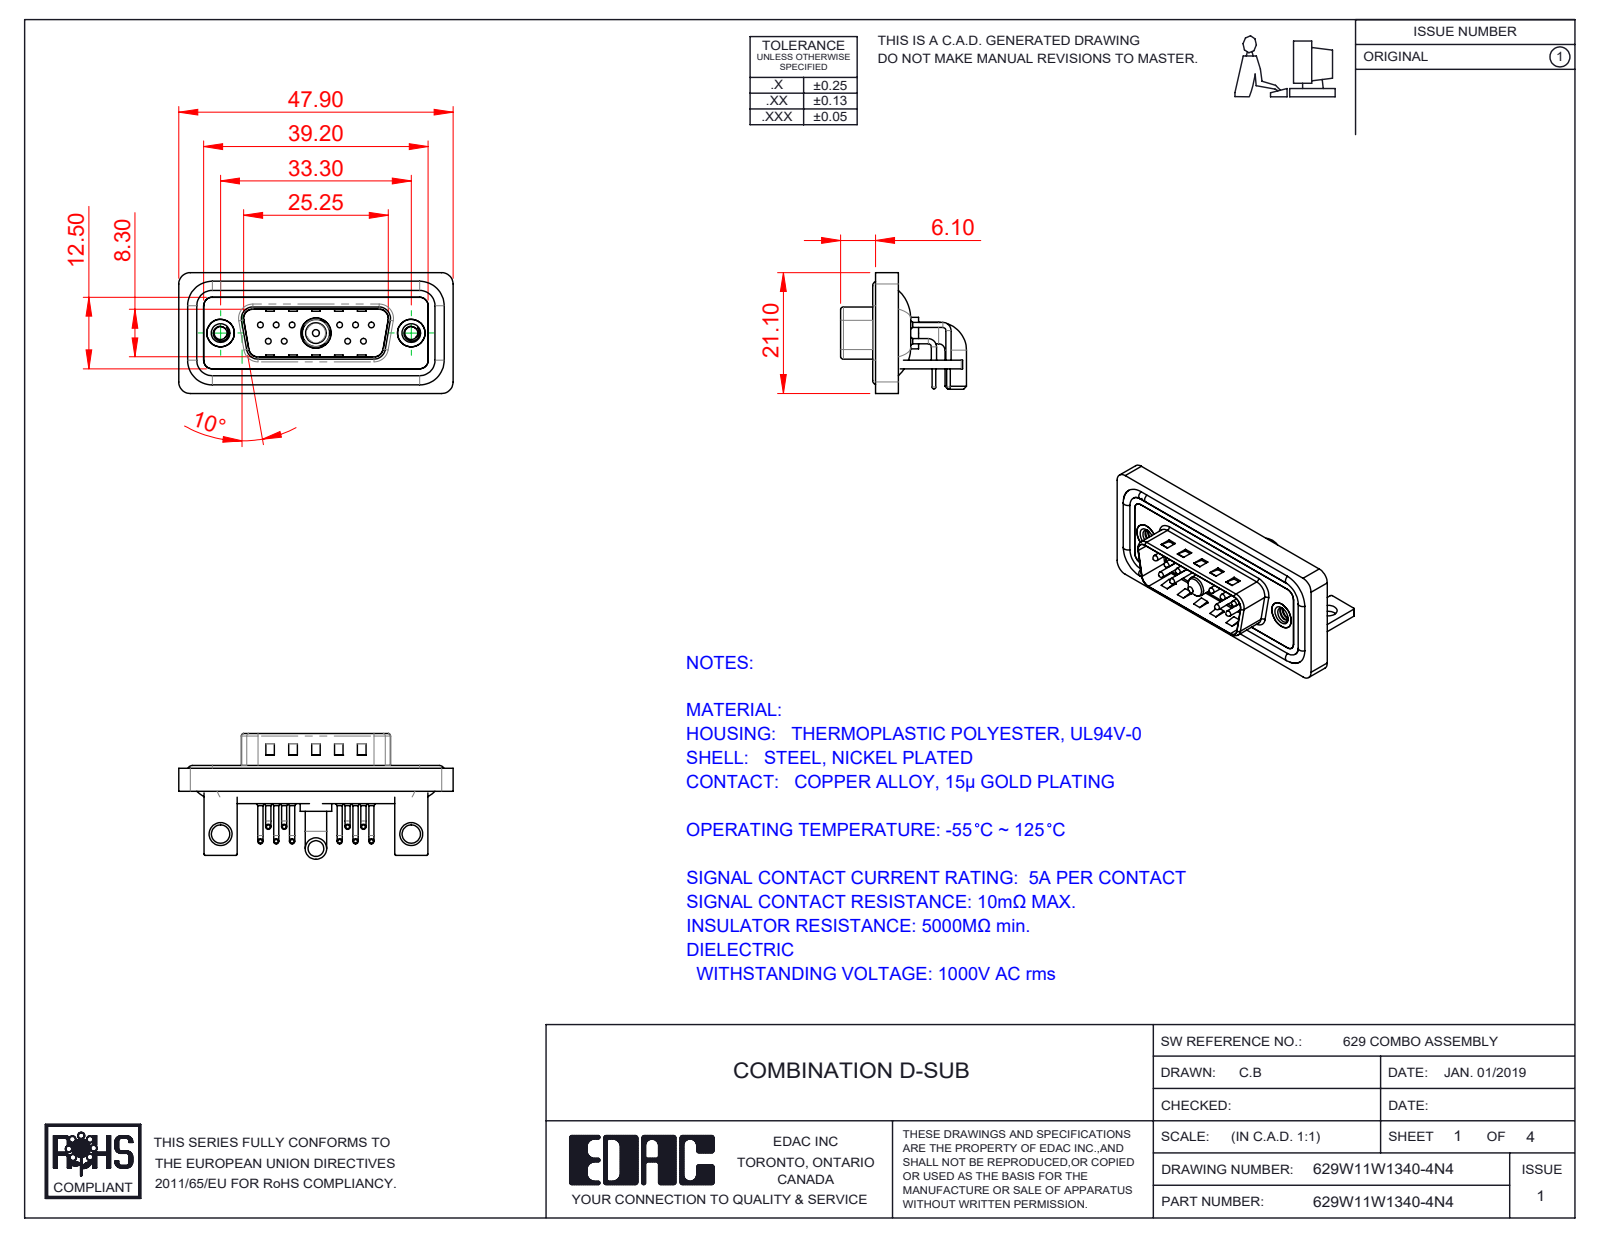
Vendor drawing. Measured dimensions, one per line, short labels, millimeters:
name: 629W11W1340-4N4; Power Pin_40A RA; 629Combo Threaded Rivet_3; 629Combo Contact Row 2 (+6 more)
written by: SolidWorks 2023 (CONFIG_CONTROL_DESIGN)
unit: mm
bodies: 21 solids, 1643 faces (856 planar, 587 cylindrical, 200 other)
size: 47.9 × 21.98 × 21.1
volume: 5 940 mm³; area: 9 911 mm²
holes: 10× ⌀0.75, 10× ⌀1.6, 10× ⌀2, 2× ⌀2.26, 2× ⌀3.2, 2× ⌀4, 2× ⌀4.8, 2× ⌀5, 1× ⌀4.85, 1× ⌀5.3
bosses: 20× ⌀0.9, 10× ⌀1.5, 10× ⌀1, 10× ⌀0.65, 4× ⌀1.6, 2× ⌀4.9, 2× ⌀3.75, 1× ⌀5.5
rounds: 21× R2, 18× R1.5, 16× R0.25, 10× R1.01, 9× R0.5, 8× R1.6, 7× R1, 4× R0.6
face distances: 0.4, 0.8, 1.5, 2.9, 2.1, 1.1, 1.6, 1.2, 3.7, 4.1
hole spacings: 3.16, 2.77, 13.85, 11.08, 16.62, 5.03, 5.04, 5.54
